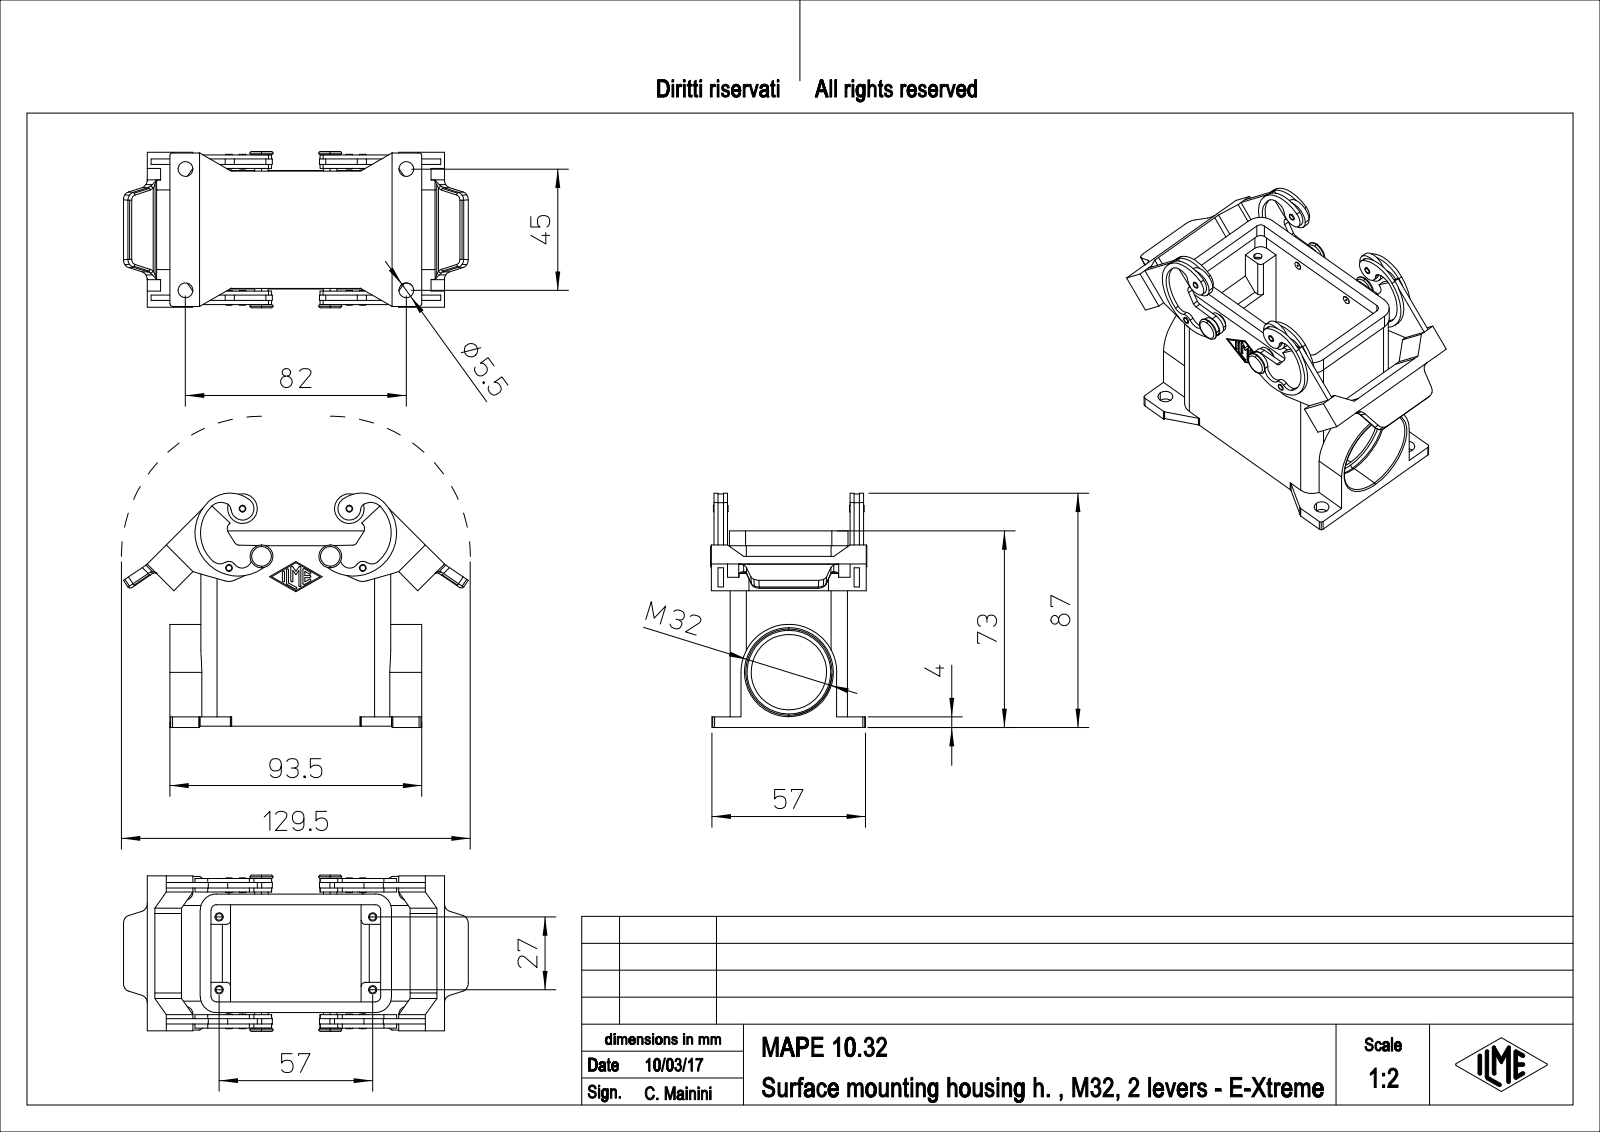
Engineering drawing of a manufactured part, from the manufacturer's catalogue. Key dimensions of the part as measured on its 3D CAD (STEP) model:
Part name (STEP PRODUCT): MAPE_10.32
STEP written by: PTC Creo Elements/Direct Modeling 19.0E 27-Jun-2016 (C) Parametric Technology GmbH (AUTOMOTIVE_DESIGN)
Units: millimetres
Bodies: 1 solid, 757 faces (329 planar, 324 cylindrical, 104 other)
Overall size (bounding box): 127.99 × 86.94 × 58
Volume: 104 421 mm³ · Surface area: 58 694 mm²
Round holes (diameter × count): ⌀2 ×4, ⌀2.46 ×4, ⌀3.1 ×4, ⌀5.5 ×4, ⌀2.5 ×2, ⌀28 ×1, ⌀32 ×1
Round bosses / shafts (diameter × count): ⌀11 ×2, ⌀5 ×2, ⌀3 ×2
Partial cylindrical surfaces — rounded edges, fillets, slot ends (radius × count): R1 ×20, R0.38 ×14, R3 ×12, R6 ×8, R1.5 ×6, R2.5 ×6, R2 ×4, R3.5 ×4
Main face-to-face distances: 3, 40.5, 4, 3.5, 43.5, 50.5, 4.5, 37.5, 11, 2.5
Hole centre spacings: 15.4, 38.11, 70.08, 78.27, 22.56, 27, 45, 49.78
